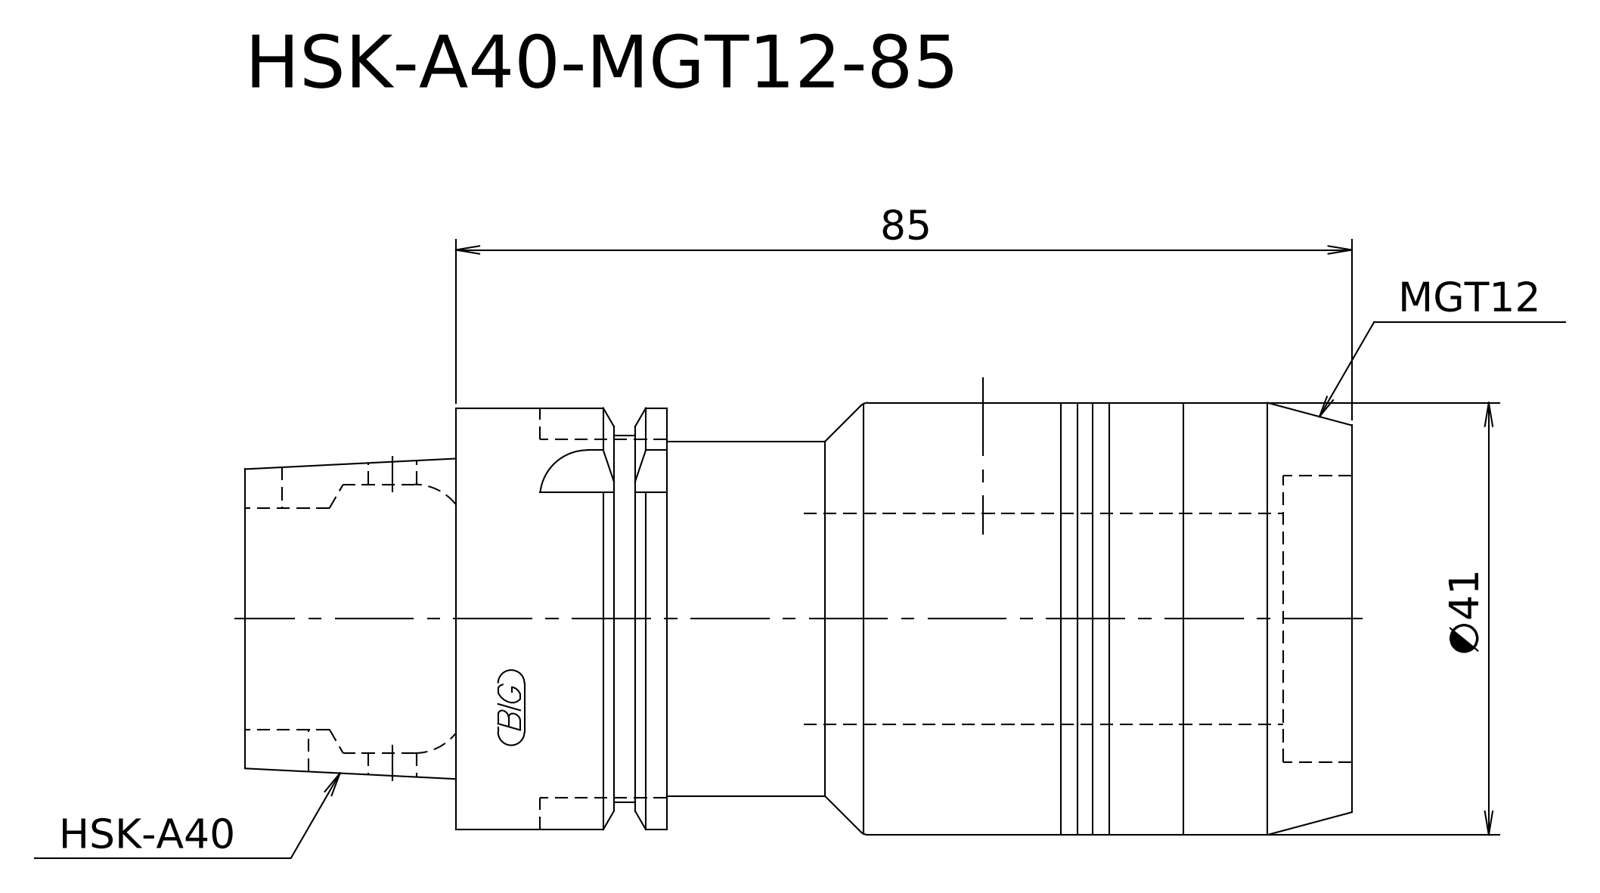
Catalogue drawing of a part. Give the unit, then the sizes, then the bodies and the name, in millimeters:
Units: millimetres
Overall size (bounding box): 105 × 41 × 41
Round bosses / shafts (diameter × count): ⌀41 ×1, ⌀40 ×1, ⌀34.8 ×1, ⌀33.6 ×1, ⌀30.2 ×1
Main face-to-face distances: 20, 105, 85, 65, 40, 68, 3, 17, 37, 70
Volume: 115 293 mm³ · Surface area: 15 493 mm²
Bodies: 1 solid, 17 faces (6 planar, 6 cylindrical, 5 other)
STEP written by: Kubotek KeyCreator V8.5.1 (14335) (CONFIG_CONTROL_DESIGN)
